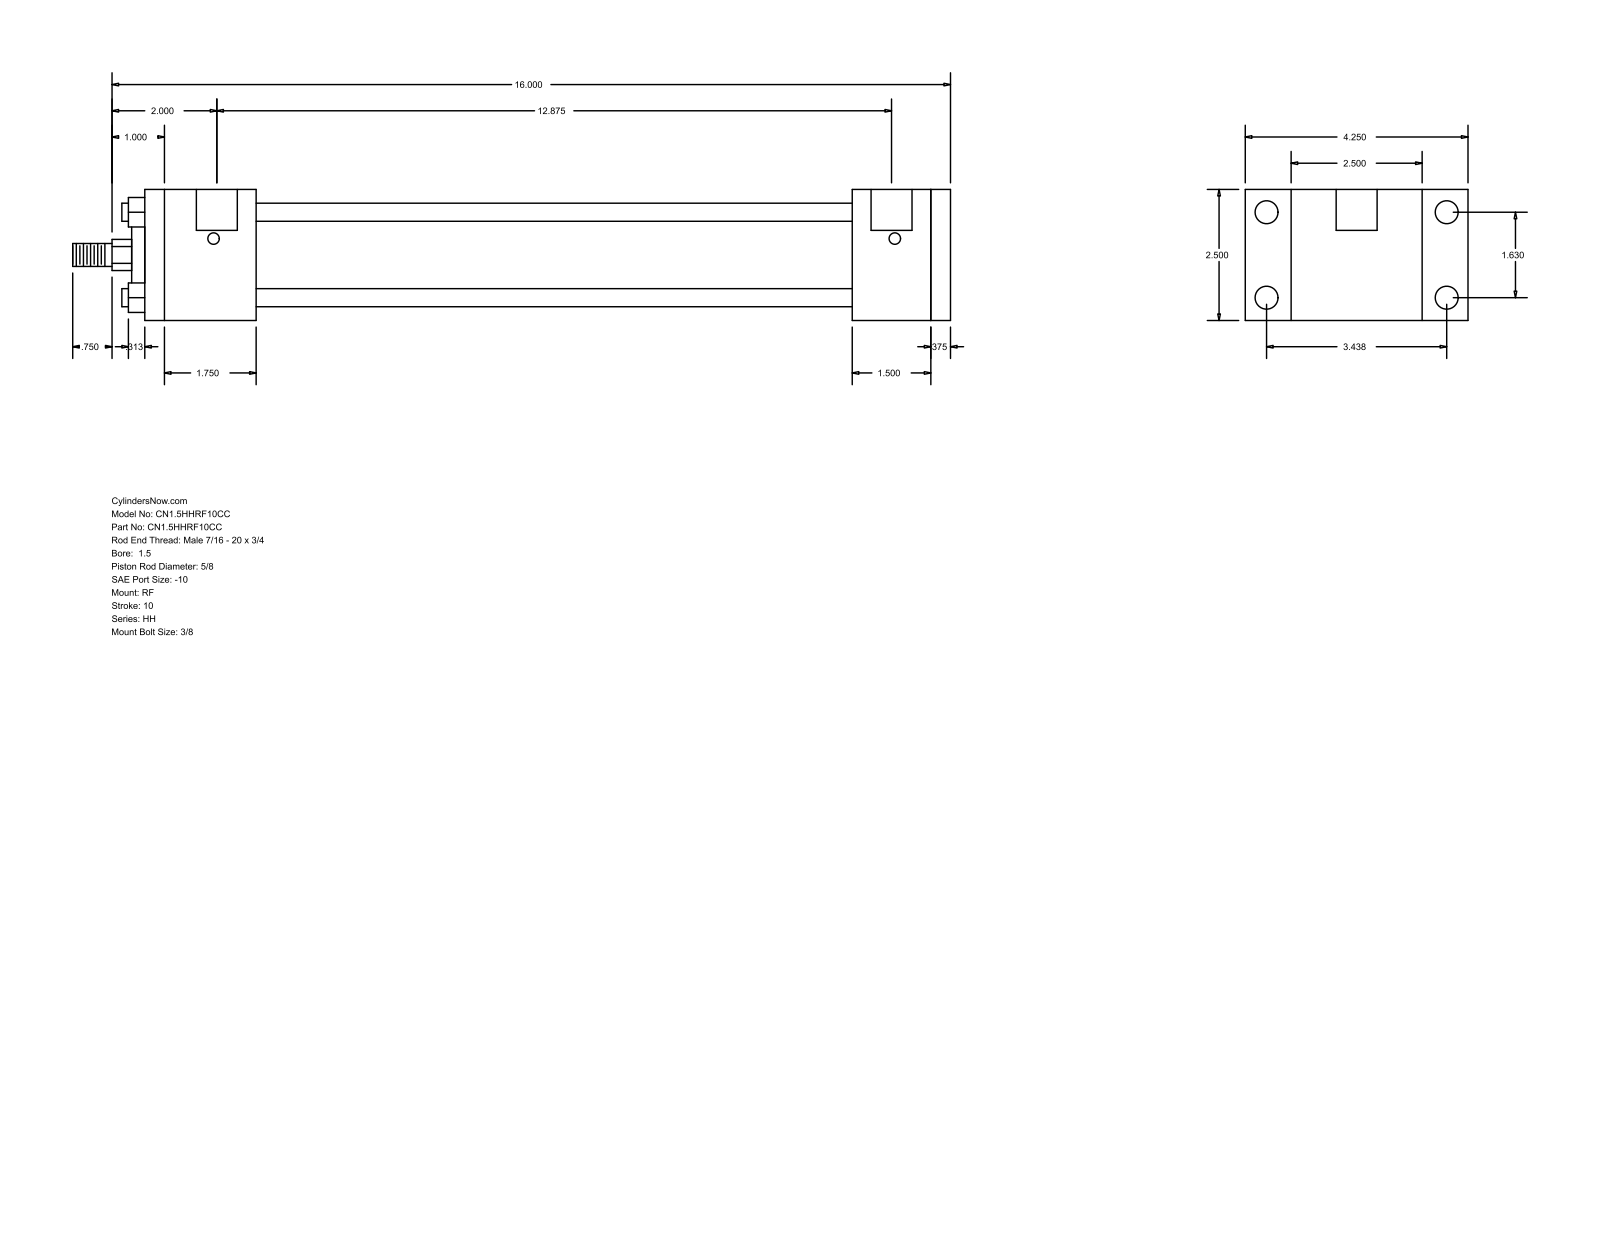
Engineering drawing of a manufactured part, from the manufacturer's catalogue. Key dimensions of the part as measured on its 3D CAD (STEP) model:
Part name (STEP PRODUCT): HH_RF__0150_0.625
STEP written by: GSSL Pune (CONFIG_CONTROL_DESIGN)
Units: millimetres
Bodies: 0 solids, 92 faces (64 planar, 28 cylindrical, 0 other)
Overall size (bounding box): 425.45 × 107.95 × 63.5
Round holes (diameter × count): ⌀5.56 ×4, ⌀11.13 ×4, ⌀19.84 ×2
Round bosses / shafts (diameter × count): ⌀8.76 ×4, ⌀44.45 ×1, ⌀28.57 ×1, ⌀15.88 ×1, ⌀11.11 ×1
Partial cylindrical surfaces — rounded edges, fillets, slot ends (radius × count): R7.54 ×1
Main face-to-face distances: 63.5, 390.52, 381, 9.52, 47.63, 53.97, 342.89, 288.92, 327.03, 336.55
Hole centre spacings: 1.59, 41.4, 87.32, 96.64, 328.61, 330.2, 327.02
